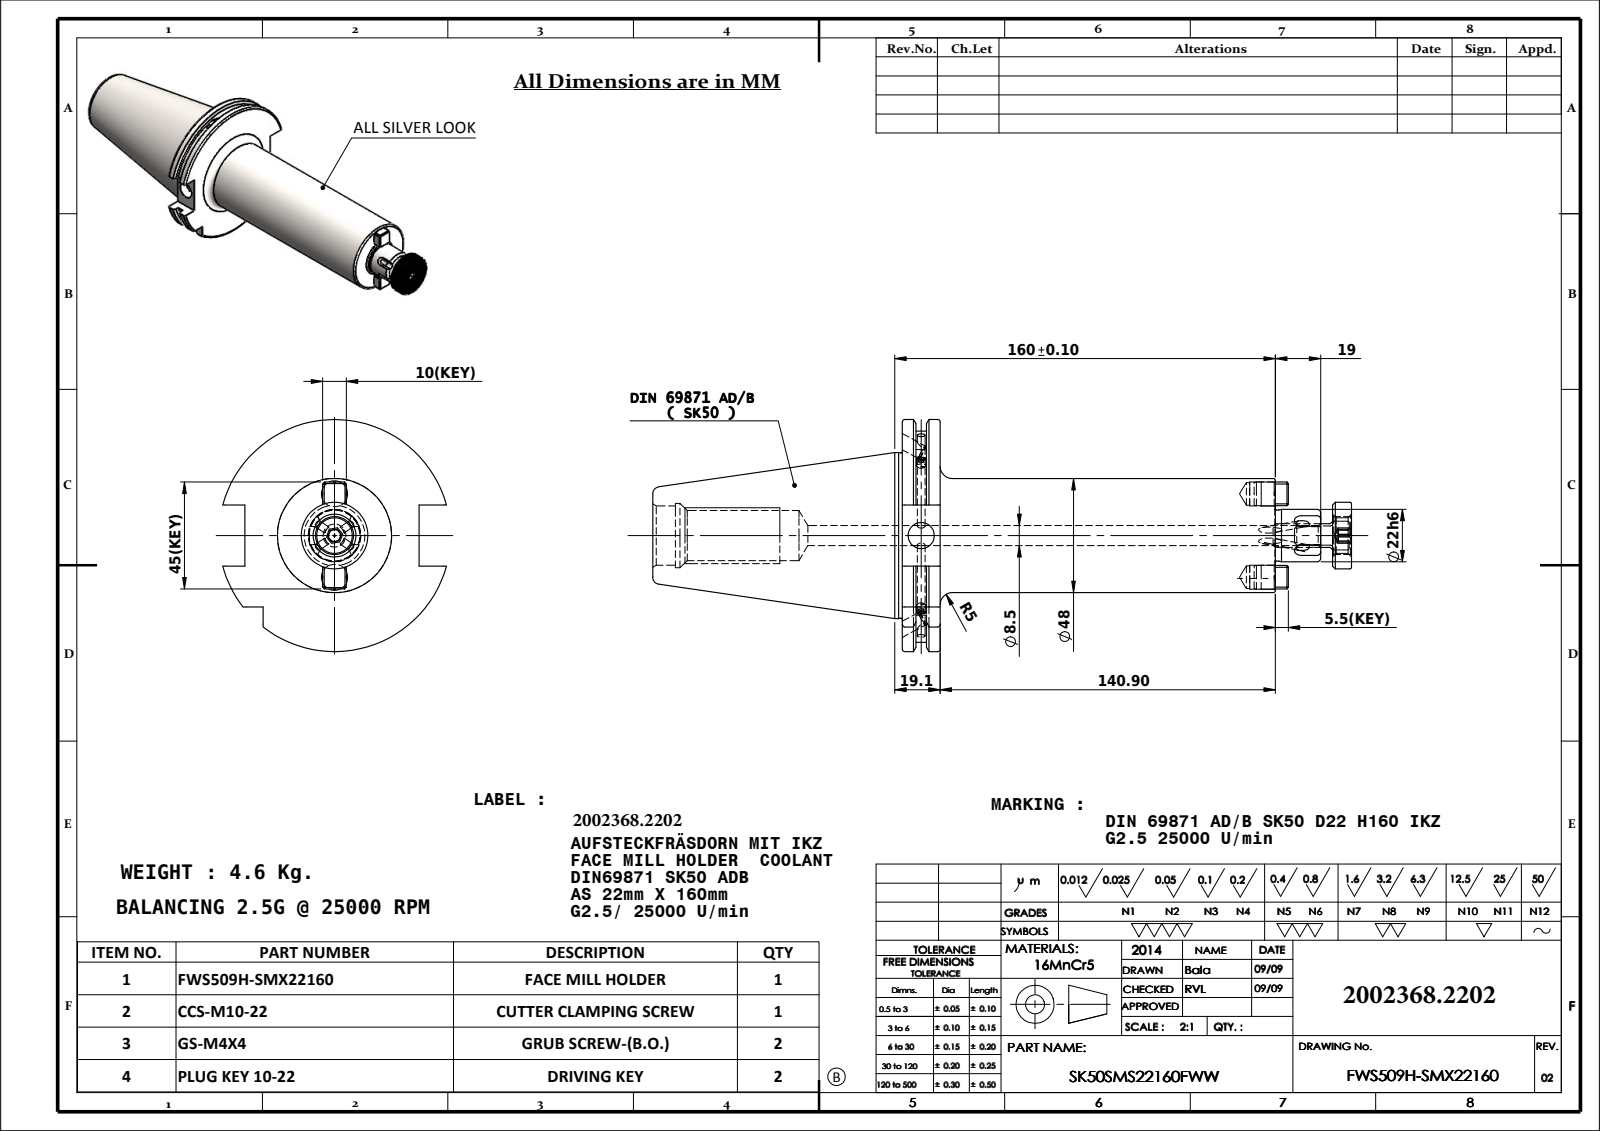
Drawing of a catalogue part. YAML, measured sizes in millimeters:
part_name: "91506-AS322 160"
step_written_by: "SolidWorks 2018 (AUTOMOTIVE_DESIGN)"
units: millimeters
bodies: {solids: 1, faces: 177, planar: 33, cylindrical: 69, other: 75}
overall_size: [280.75, 97.5, 94.05]
volume: 585294
surface_area: 70818
round_holes:
  - {diameter: 3, count: 4}
  - {diameter: 6, count: 2}
  - {diameter: 9.5, count: 2}
  - {diameter: 10, count: 2}
  - {diameter: 3.3, count: 1}
  - {diameter: 8.5, count: 1}
  - {diameter: 11, count: 1}
  - {diameter: 21, count: 1}
  - {diameter: 25, count: 1}
  - {diameter: 27, count: 1}
round_bosses_or_shafts:
  - {diameter: 69.85, count: 1}
  - {diameter: 69.45, count: 1}
  - {diameter: 48, count: 1}
  - {diameter: 22, count: 1}
  - {diameter: 21.4, count: 1}
partial_cylinders:
  - {radius: 2, count: 4}
  - {radius: 44.9, count: 1}
  - {radius: 48.75, count: 1}
face_to_face_distances: [15.9, 156.8, 140.9, 5.66, 10.24, 151.14, 10.14, 4.48, 5.76, 146.66]
hole_center_spacings: [17.5, 35]
